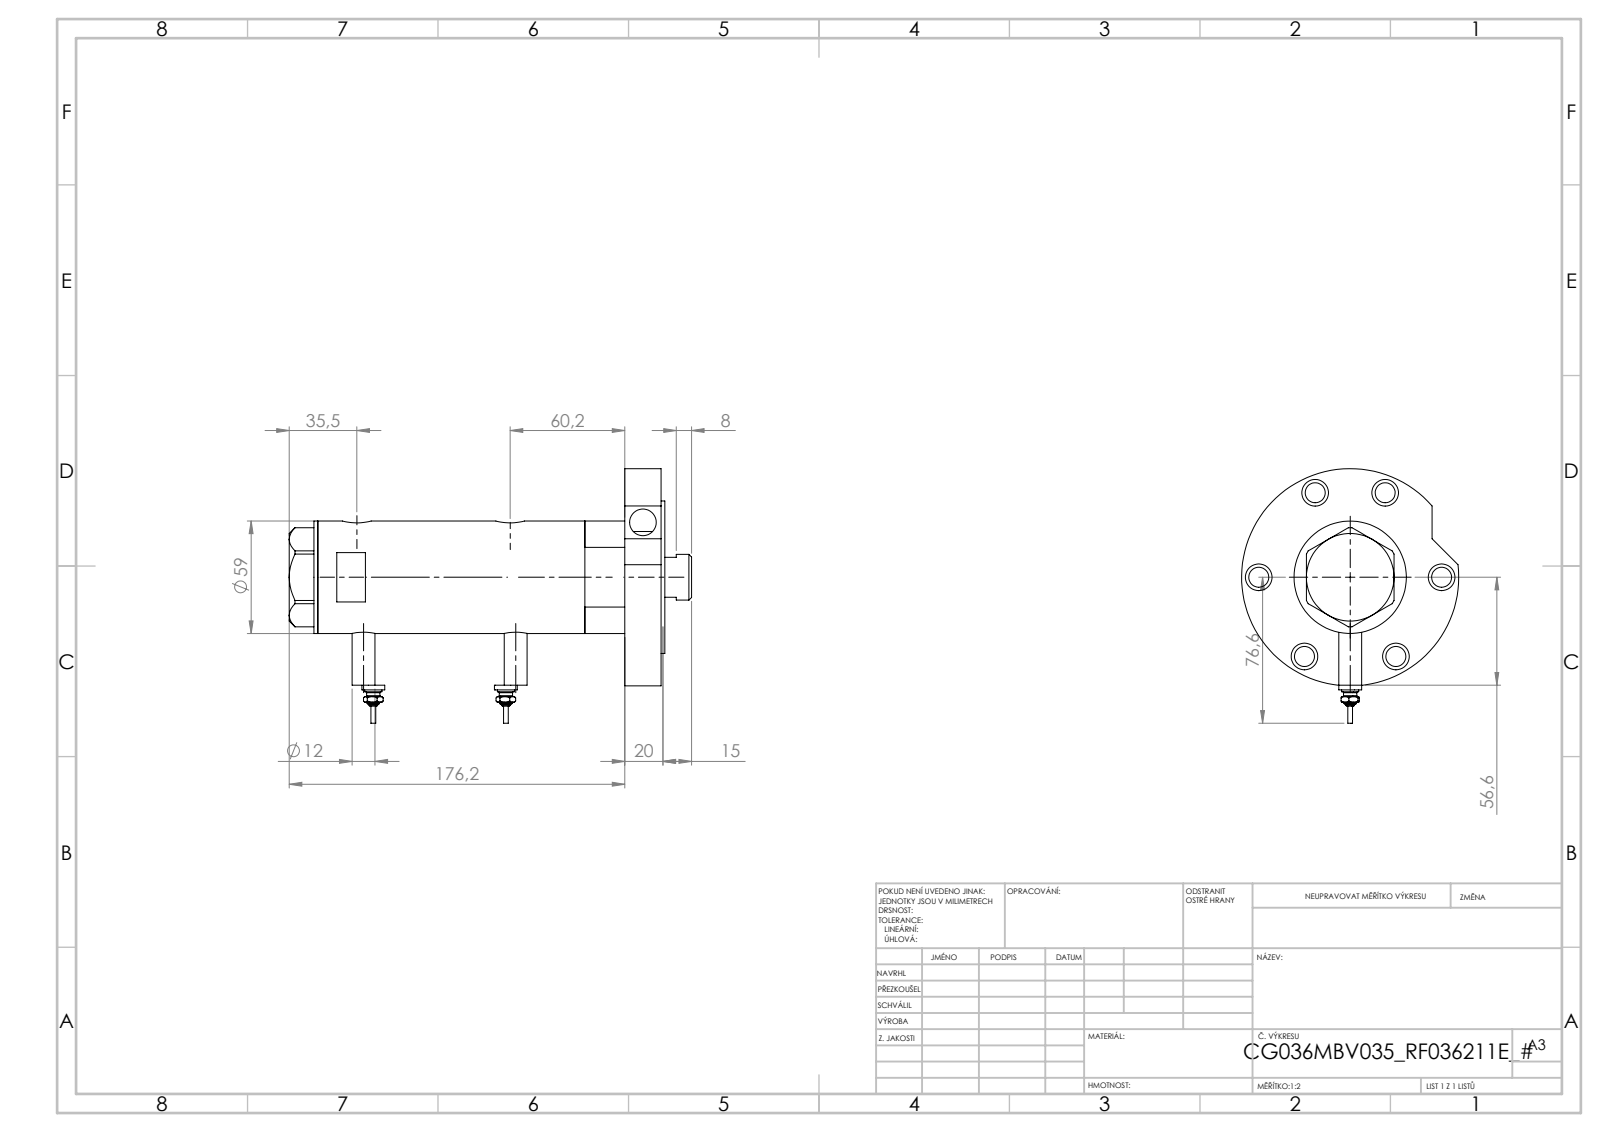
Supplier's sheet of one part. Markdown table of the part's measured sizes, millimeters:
| quantity | value |
| --- | --- |
| part name | V270CG_MIDDLE; V270CG_RF211E; V270CG_FRONT; V270CG_VC (+2 more) |
| STEP written by | SolidWorks 2019 (CONFIG_CONTROL_DESIGN) |
| units | millimeters |
| bodies | 7 solids, 276 faces (92 planar, 110 cylindrical, 74 other) |
| overall size | 198.42 × 118.8 × 114 |
| volume | 587 424 mm³ |
| surface area | 130 506 mm² |
| round holes (diameter × count) | 14 × 7, 10.5 × 6, 5 × 2, 9.73 × 2, 12.5 × 2, 15 × 2, 8.5 × 1, 25 × 1, 26.5 × 1, 36 × 1, 40 × 1, 48 × 1 |
| round bosses / shafts (diameter × count) | 12 × 3, 9 × 2, 7 × 2, 4.34 × 2, 2.4 × 2, 114 × 1, 80 × 1, 59 × 1 |
| main face-to-face distances | 19, 2, 166.84, 21, 145.84, 164.84, 92.34, 53.5, 72.5, 74.5 |
| hole center spacings | 48, 2.9, 3.5, 53.34, 67.15, 70.05, 70.65, 73.55 |
